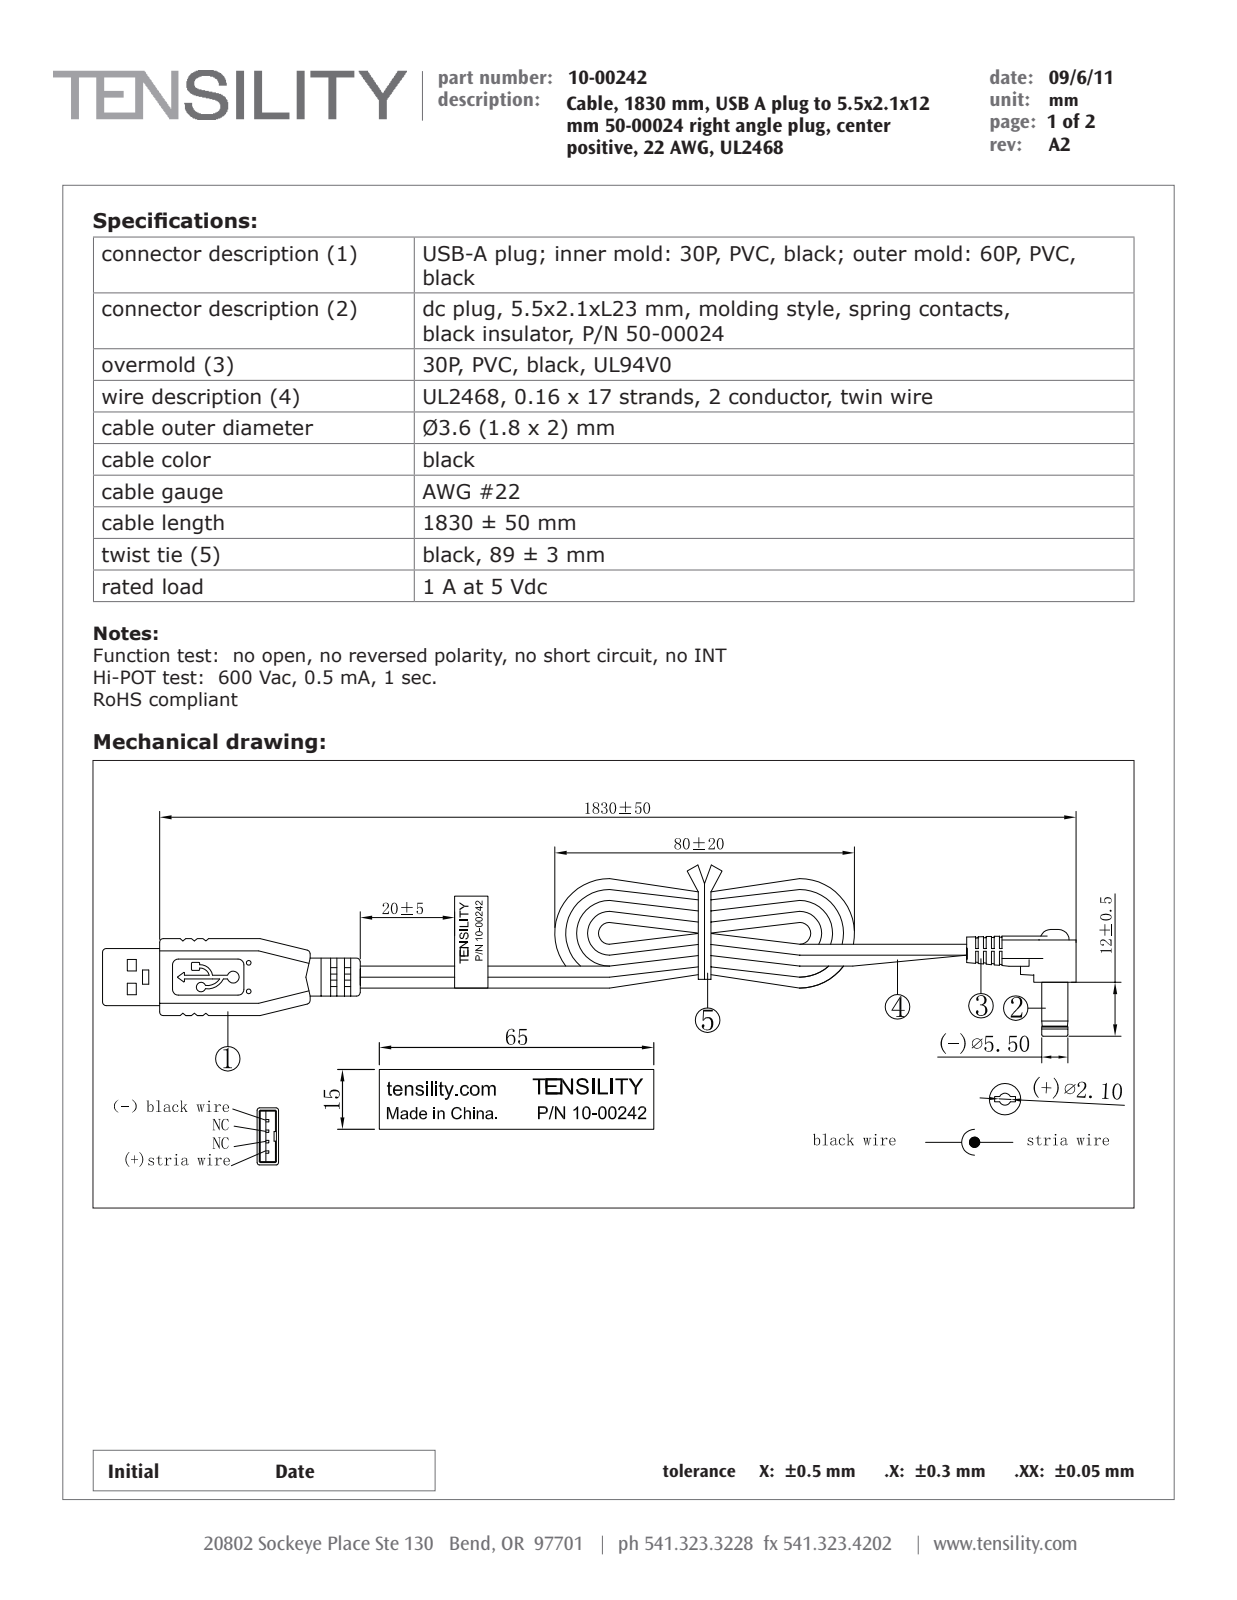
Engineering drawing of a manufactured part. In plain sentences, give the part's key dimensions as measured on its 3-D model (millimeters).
The part is named "24-00046_default; 30-00008_wbc; 50-00186; 50-00425 shell (+8 more)". Its 3-D file was written by "SolidWorks 2015 (AUTOMOTIVE_DESIGN)". It is 60 solids with 1187 faces: 629 planar, 325 cylindrical and 233 other. Overall it measures 211.6 by 48.7 by 8.4 millimeters. Its volume is 7 485 cubic millimeters and its surface area 13 464 square millimeters. Round holes: 2 of diameter 0.85, 1 of diameter 1.5, 1 of diameter 4.8, 1 of diameter 5.5. Round bosses or shafts: 2 of diameter 8, 2 of diameter 1.9, 1 of diameter 7.26, 1 of diameter 6.1, 1 of diameter 5.48, 1 of diameter 5.3, 1 of diameter 4, 1 of diameter 2.82. Partial cylindrical surfaces (rounded edges, fillets, slot ends): 56 of radius 0.1, 12 of radius 0.2, 10 of radius 0.5, 8 of radius 0.75, 6 of radius 0.3, 4 of radius 0.15, 4 of radius 0.25, 4 of radius 0.64. The main face-to-face distances are 0.5, 1.95, 1.86, 1.81, 2.01, 6.45, 2.33, 0.32, 4.28, 3.87. The hole center spacings are 1.78.
